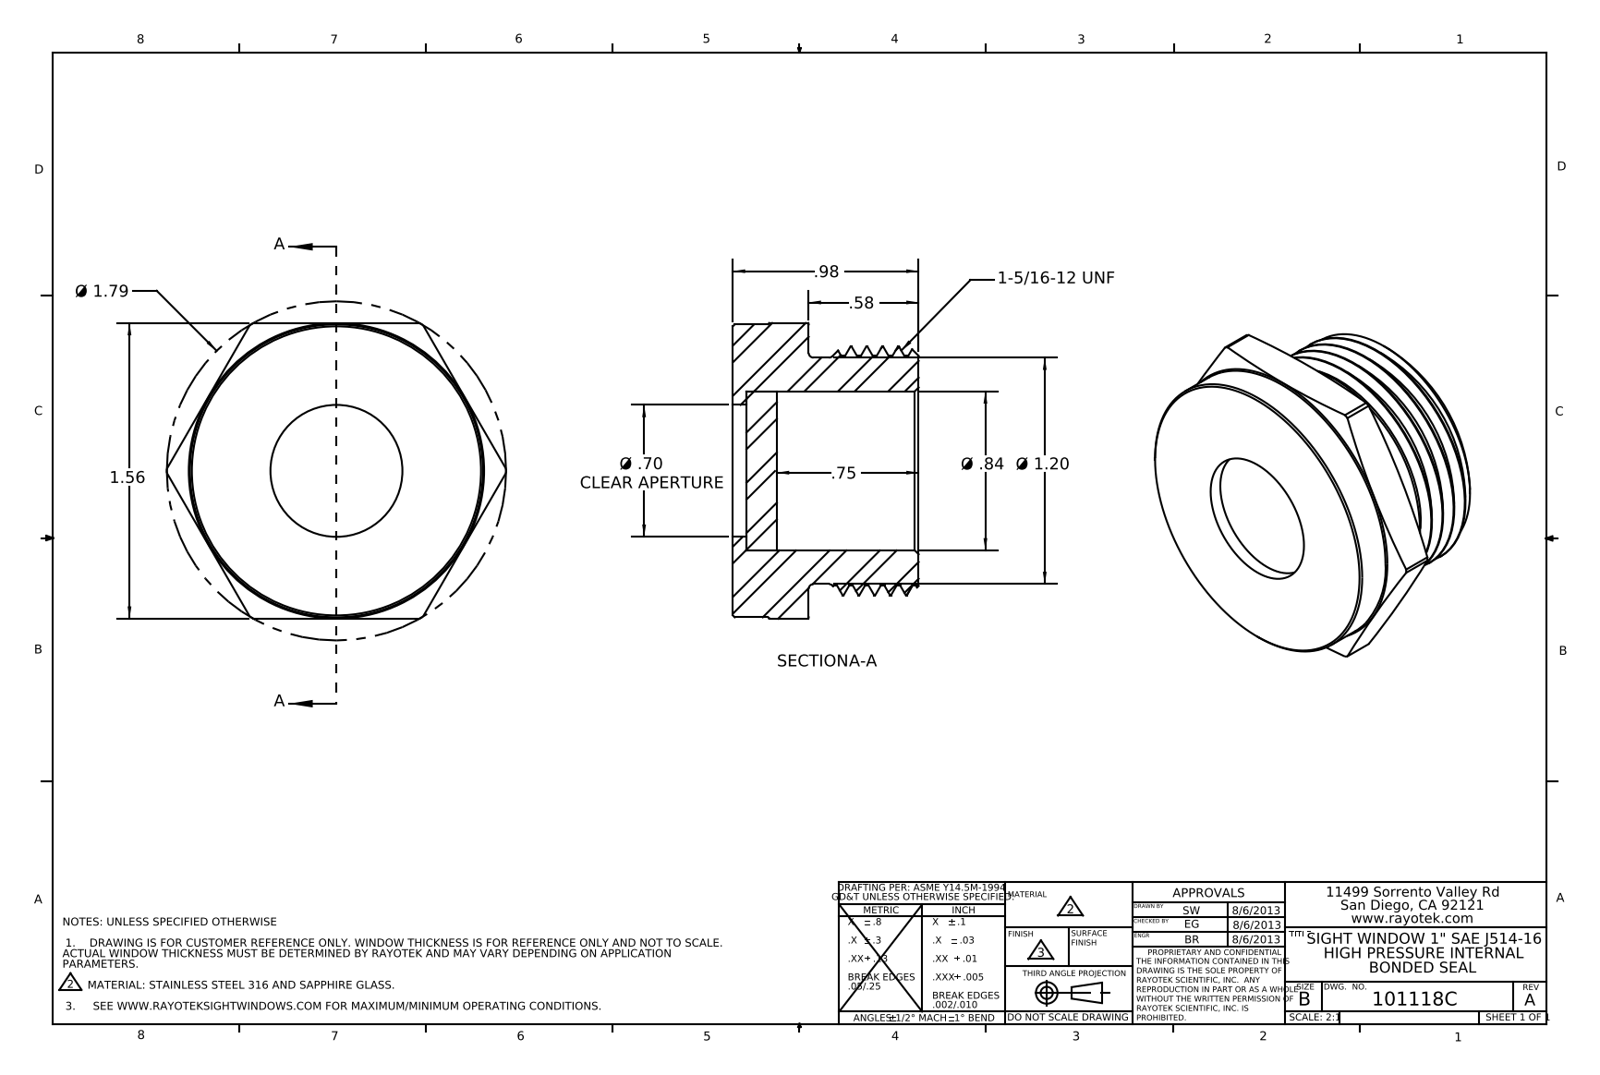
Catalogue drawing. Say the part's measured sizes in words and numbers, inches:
The part is named "403118". Its 3-D file was written by "SolidWorks 2012 (AUTOMOTIVE_DESIGN)". It is 2 solids with 61 faces: 12 planar, 26 cylindrical and 23 other. Overall it measures 1.789 by 1.56 by 0.98 inches. Its volume is 1.052 cubic inches and its surface area 12.85 square inches. Round holes: 1 of diameter 0.696, 1 of diameter 0.84. Round bosses or shafts: 1 of diameter 1.545, 1 of diameter 1.313, 1 of diameter 1.195. Partial cylindrical surfaces (rounded edges, fillets, slot ends): 1 of radius 0.895. The main face-to-face distances are 0.072, 0.328, 0.4, 0.168, 0.16, 0.232, 0.58, 0.748, 0.908, 0.98.
